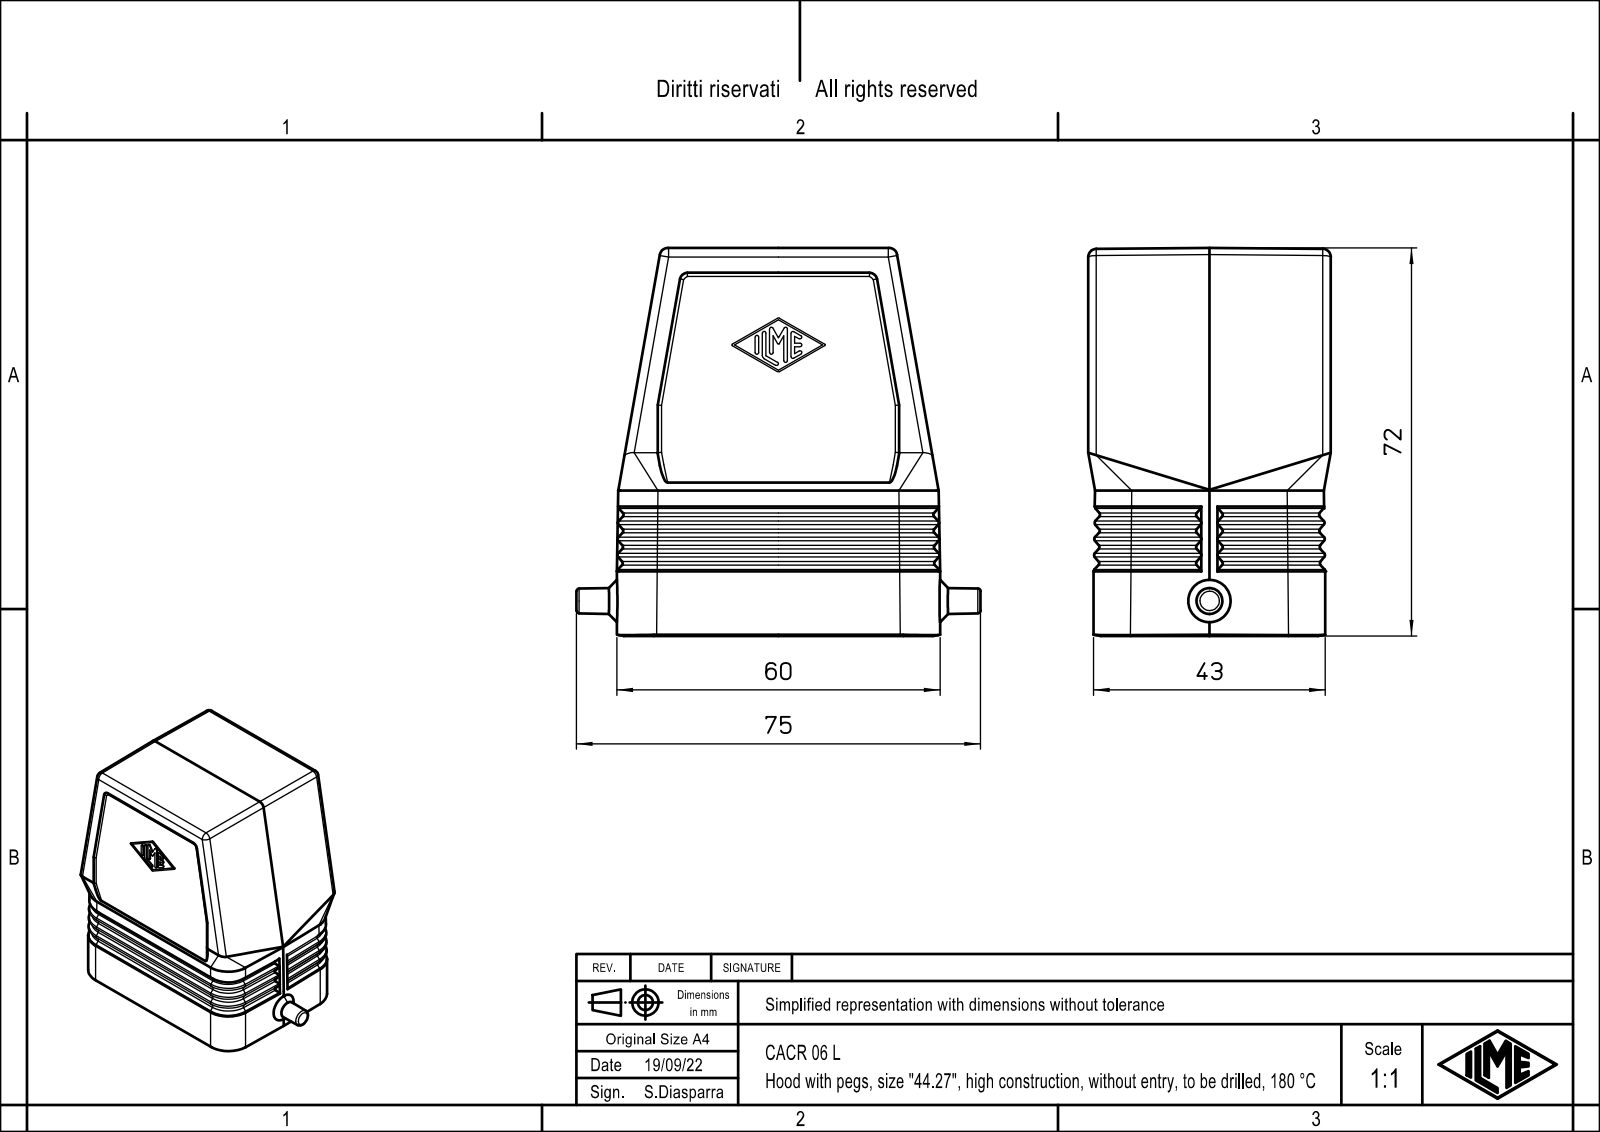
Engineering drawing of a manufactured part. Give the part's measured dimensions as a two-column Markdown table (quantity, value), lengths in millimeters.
| quantity | value |
| --- | --- |
| part name | CACR 06 L |
| STEP written by | Creo Elements/Direct Modeling 20.1B 02-Apr-2019 (C) Parametric Technology GmbH (AUTOMOTIVE_DESIGN) |
| units | millimeters |
| bodies | 1 solid, 481 faces (185 planar, 150 cylindrical, 146 other) |
| overall size | 75 × 72 × 45 |
| volume | 64 286 mm³ |
| surface area | 28 923 mm² |
| partial cylindrical surfaces (radius × count) | 0.5 × 54, 1 × 28, 1.5 × 19, 0.33 × 15, 7 × 8, 2 × 5, 3 × 4, 4.2 × 4 |
| main face-to-face distances | 43, 2.01, 7.95, 2, 1, 44, 8.5, 45, 4.01, 4 |
